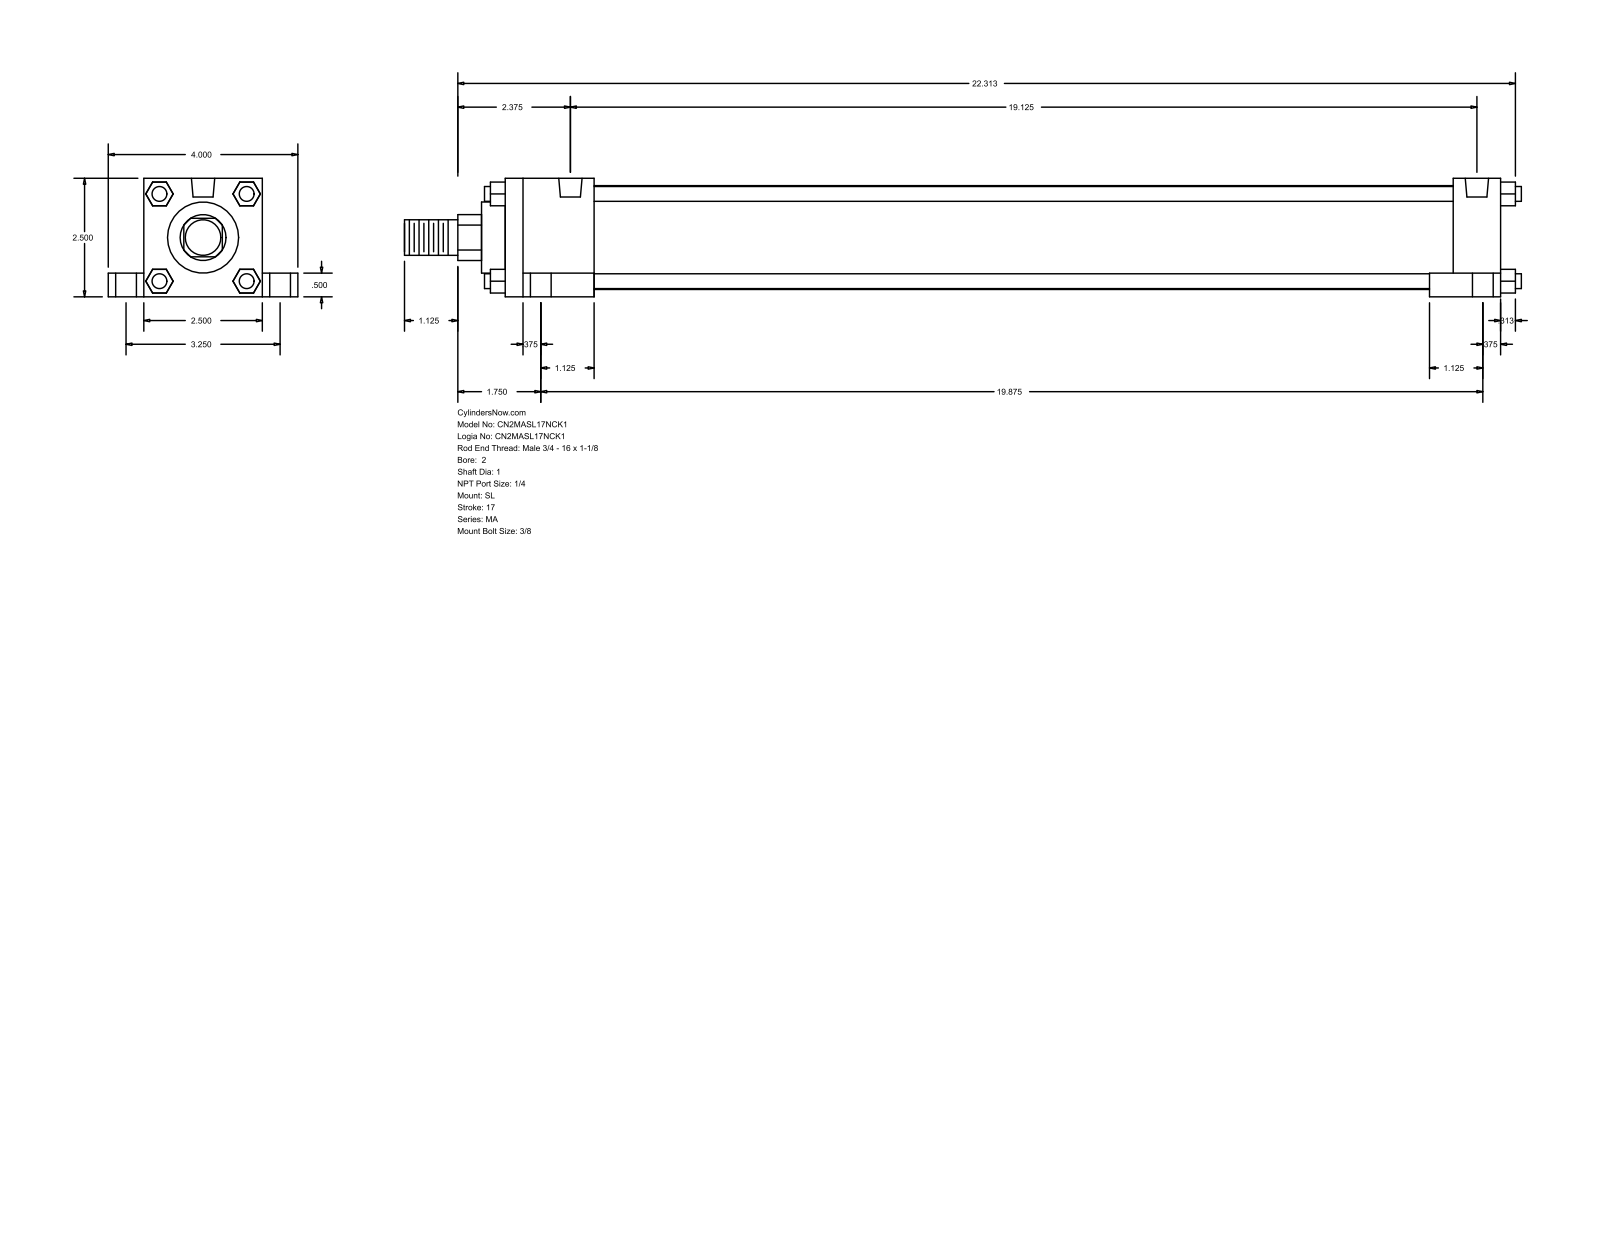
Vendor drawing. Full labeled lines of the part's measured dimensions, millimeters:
Part name (STEP PRODUCT): MA_SL__0200_1
STEP written by: GSSL Pune (CONFIG_CONTROL_DESIGN)
Units: millimetres
Bodies: 0 solids, 148 faces (112 planar, 36 cylindrical, 0 other)
Overall size (bounding box): 598.49 × 101.6 × 63.5
Round holes (diameter × count): ⌀7.94 ×4, ⌀11.11 ×4, ⌀17.46 ×4, ⌀12.49 ×2
Round bosses / shafts (diameter × count): ⌀7.94 ×4, ⌀55.63 ×1, ⌀38.1 ×1, ⌀25.4 ×1, ⌀19.05 ×1
Partial cylindrical surfaces — rounded edges, fillets, slot ends (radius × count): R12.29 ×1
Main face-to-face distances: 63.5, 12.7, 533.4, 19.05, 82.55, 25.4, 50.8, 47.63, 485.77, 508
Hole centre spacings: 41.39, 44.22, 82.54, 485.77, 490.68, 503.34, 504.82, 511.52
